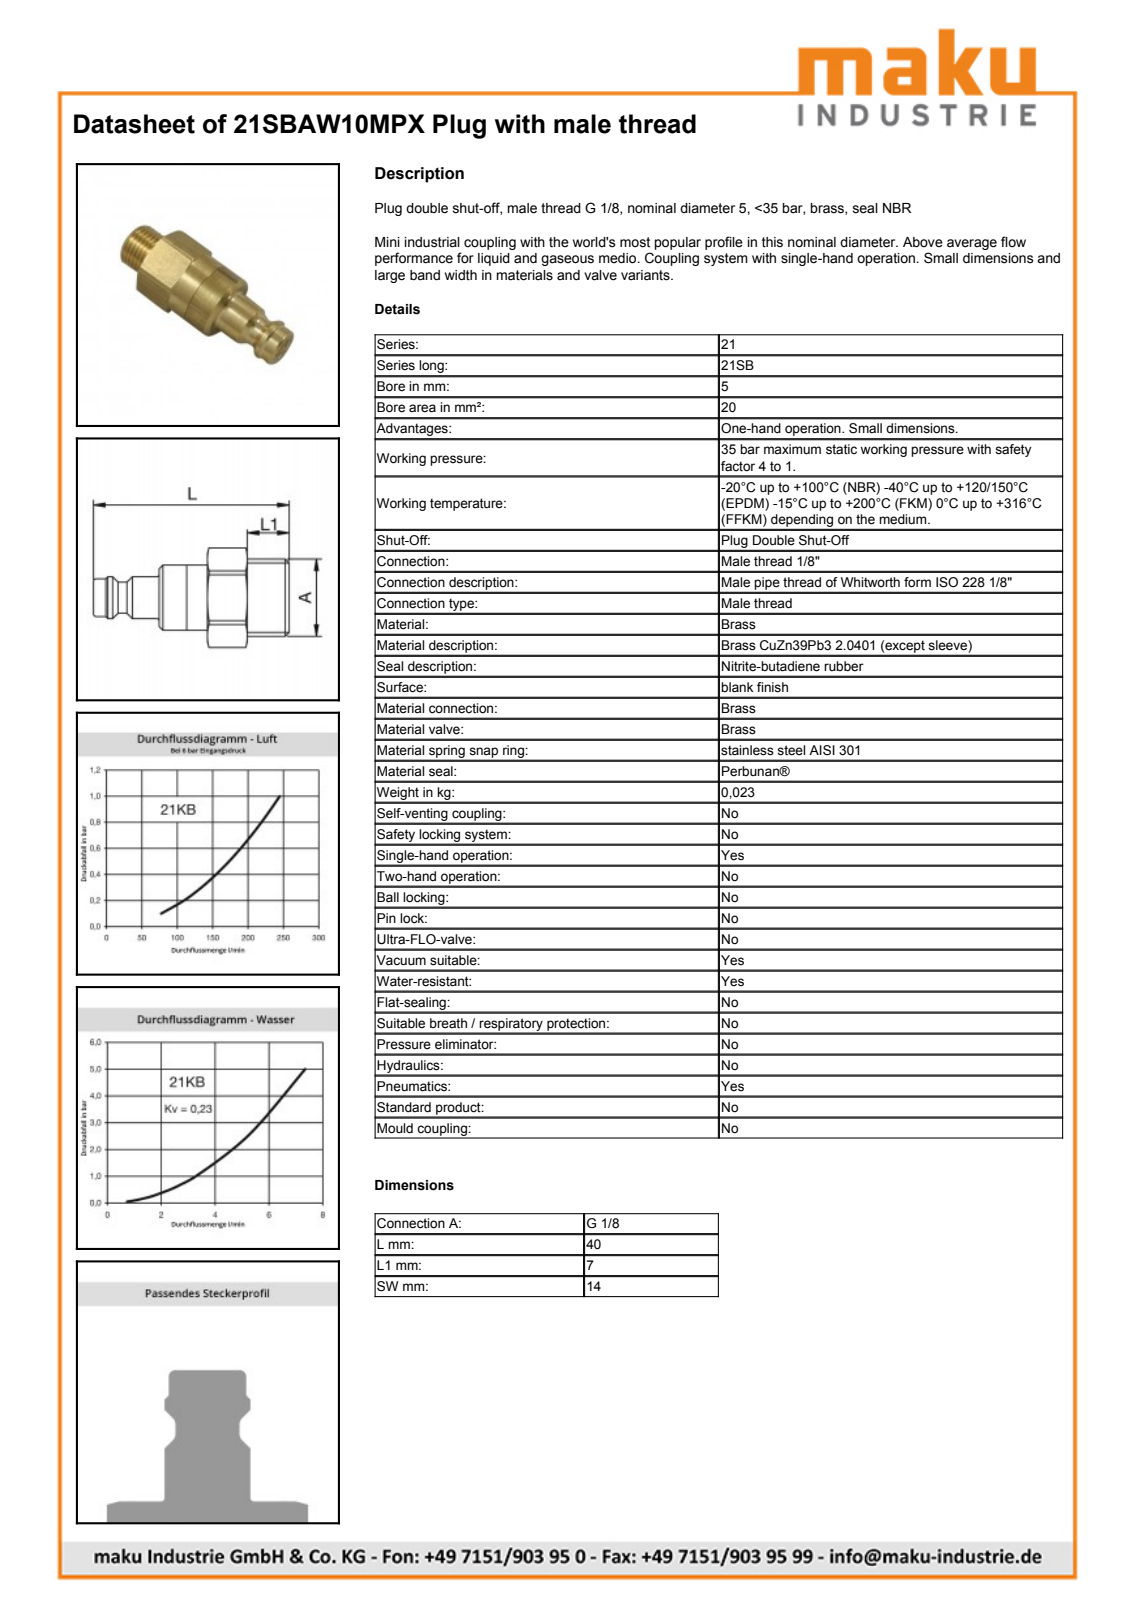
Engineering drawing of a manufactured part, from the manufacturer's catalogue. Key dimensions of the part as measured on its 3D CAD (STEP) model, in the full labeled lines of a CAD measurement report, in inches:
Part name (STEP PRODUCT): D106293
STEP written by: Autodesk Inventor 2011 (AUTOMOTIVE_DESIGN)
Units: inches
Bodies: 1 solid, 52 faces (11 planar, 16 cylindrical, 25 other)
Overall size (bounding box): 1.575 × 0.619 × 0.588
Volume: 0.261 in³ · Surface area: 3.36 in²
Round holes (diameter × count): ⌀0.472 ×1
Round bosses / shafts (diameter × count): ⌀0.551 ×1, ⌀0.472 ×1, ⌀0.442 ×1, ⌀0.383 ×1, ⌀0.354 ×1, ⌀0.319 ×1, ⌀0.262 ×1
Partial cylindrical surfaces — rounded edges, fillets, slot ends (radius × count): R0.311 ×1
Main face-to-face distances: 0.551, 0.276, 0.744, 1.02, 0.555, 1.299, 1.575, 0.945, 0.39, 0.354
